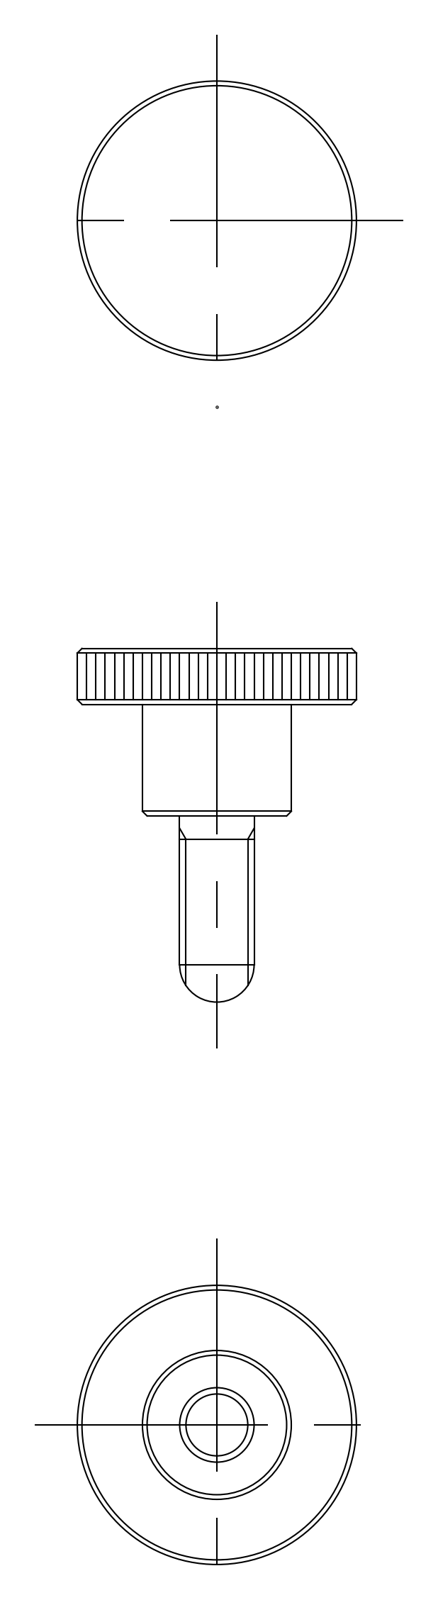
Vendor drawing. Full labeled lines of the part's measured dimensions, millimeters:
Part name (STEP PRODUCT): knob
STEP written by: CADfix (AUTOMOTIVE_DESIGN)
Units: millimetres
Bodies: 1 solid, 16 faces (0 planar, 0 cylindrical, 16 other)
Overall size (bounding box): 38 × 30 × 30
Volume: 7 576 mm³ · Surface area: 2 965 mm²
